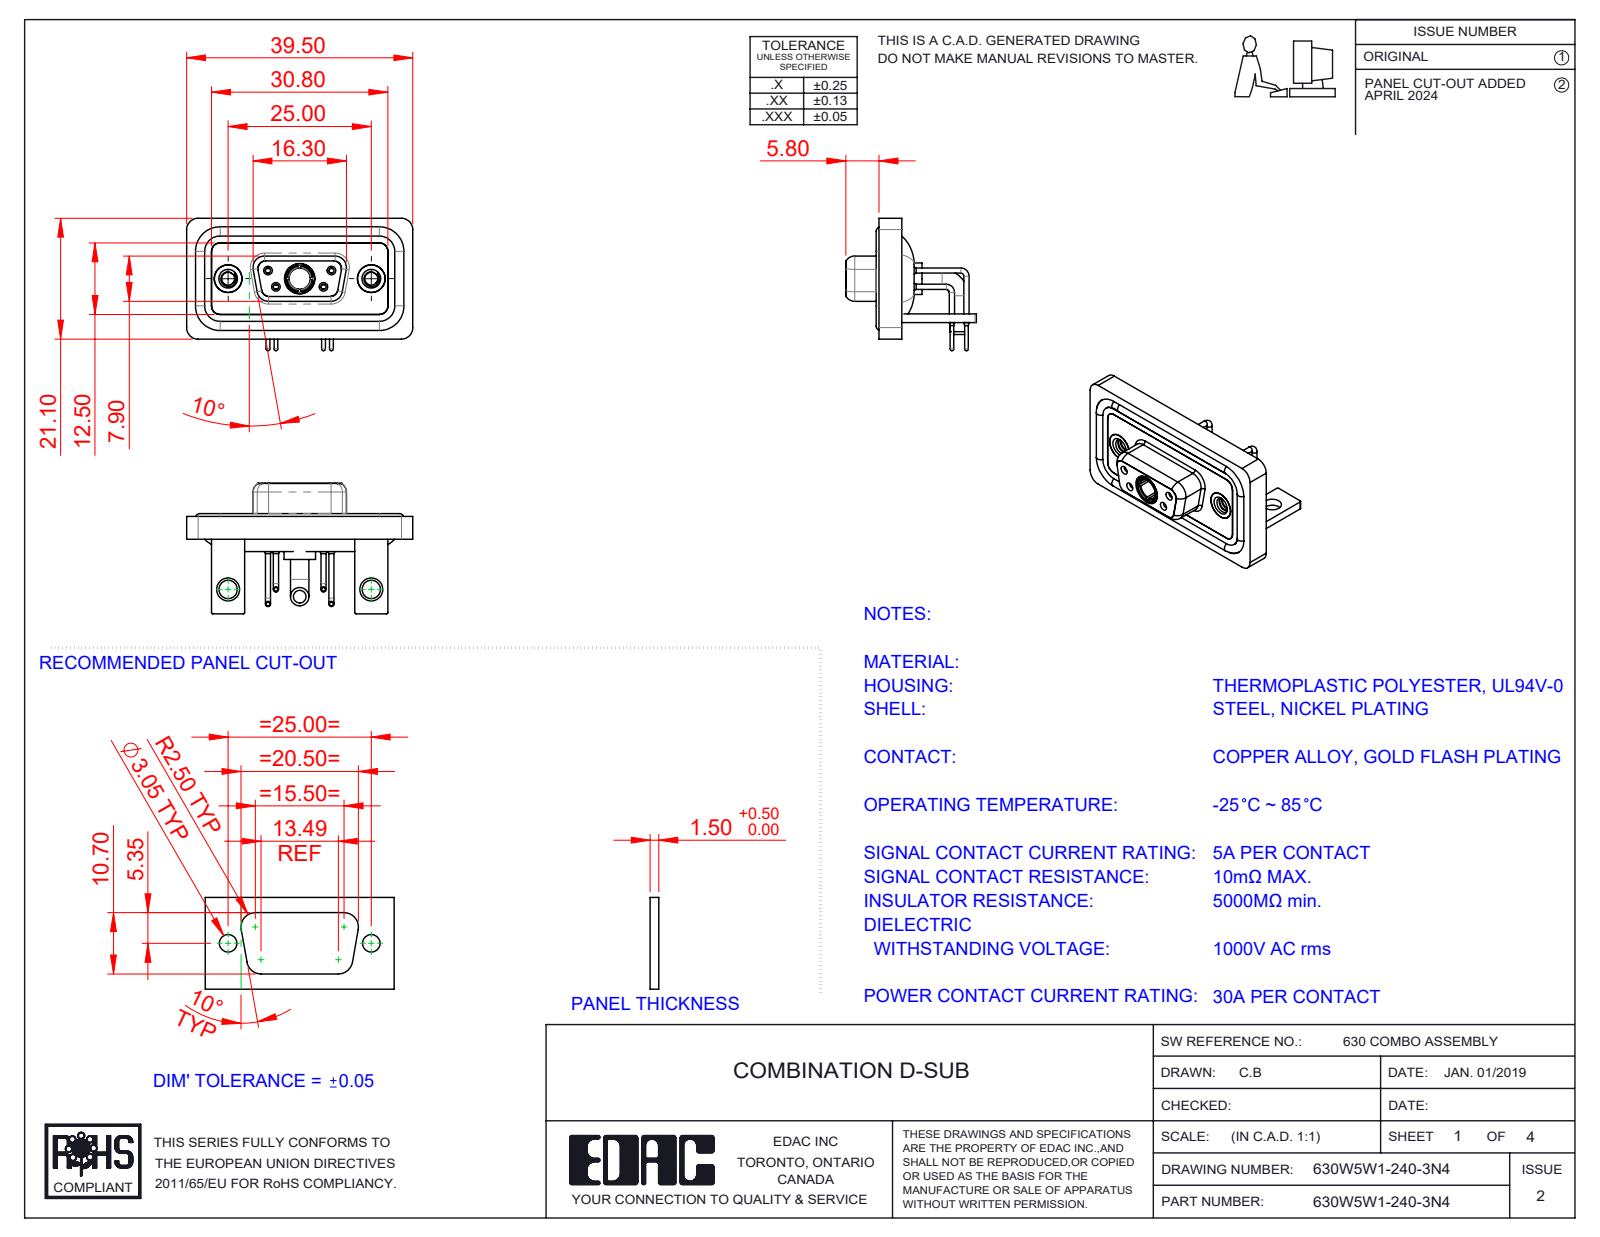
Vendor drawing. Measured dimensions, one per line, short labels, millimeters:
name: 630W5W1-240-3N4; 630Combo Shell Front_09 Contacts; 630Combo Waterproof Housing_09 Contacts; 630Combo Threaded Rivet_2 (+6 more)
written by: SolidWorks 2023 (CONFIG_CONTROL_DESIGN)
unit: mm
bodies: 15 solids, 724 faces (214 planar, 329 cylindrical, 181 other)
size: 39.5 × 23.12 × 22.8
volume: 5 223 mm³; area: 8 597 mm²
holes: 4× ⌀0.9, 4× ⌀1.1, 4× ⌀1.5, 4× ⌀2, 3× ⌀4.85, 2× ⌀1.6, 2× ⌀1.7, 2× ⌀2.26, 2× ⌀3.2, 2× ⌀4, 2× ⌀4.05, 2× ⌀5
bosses: 6× ⌀1.6, 4× ⌀0.9, 4× ⌀0.65, 2× ⌀4.95, 2× ⌀4.8, 2× ⌀3.2, 1× ⌀5.5, 1× ⌀5.2
rounds: 19× R2, 18× R1.5, 16× R0.25, 8× R1.35, 8× R1.6, 5× R0.5, 4× R0.6, 4× R0.65
face distances: 0.4, 2.9, 1.5, 1.8, 1.1, 3.7, 1.6, 0.8, 2.5, 3.1
hole spacings: 3.16, 5.72, 7.1, 12.5, 18.1, 25, 4.39, 4.4
